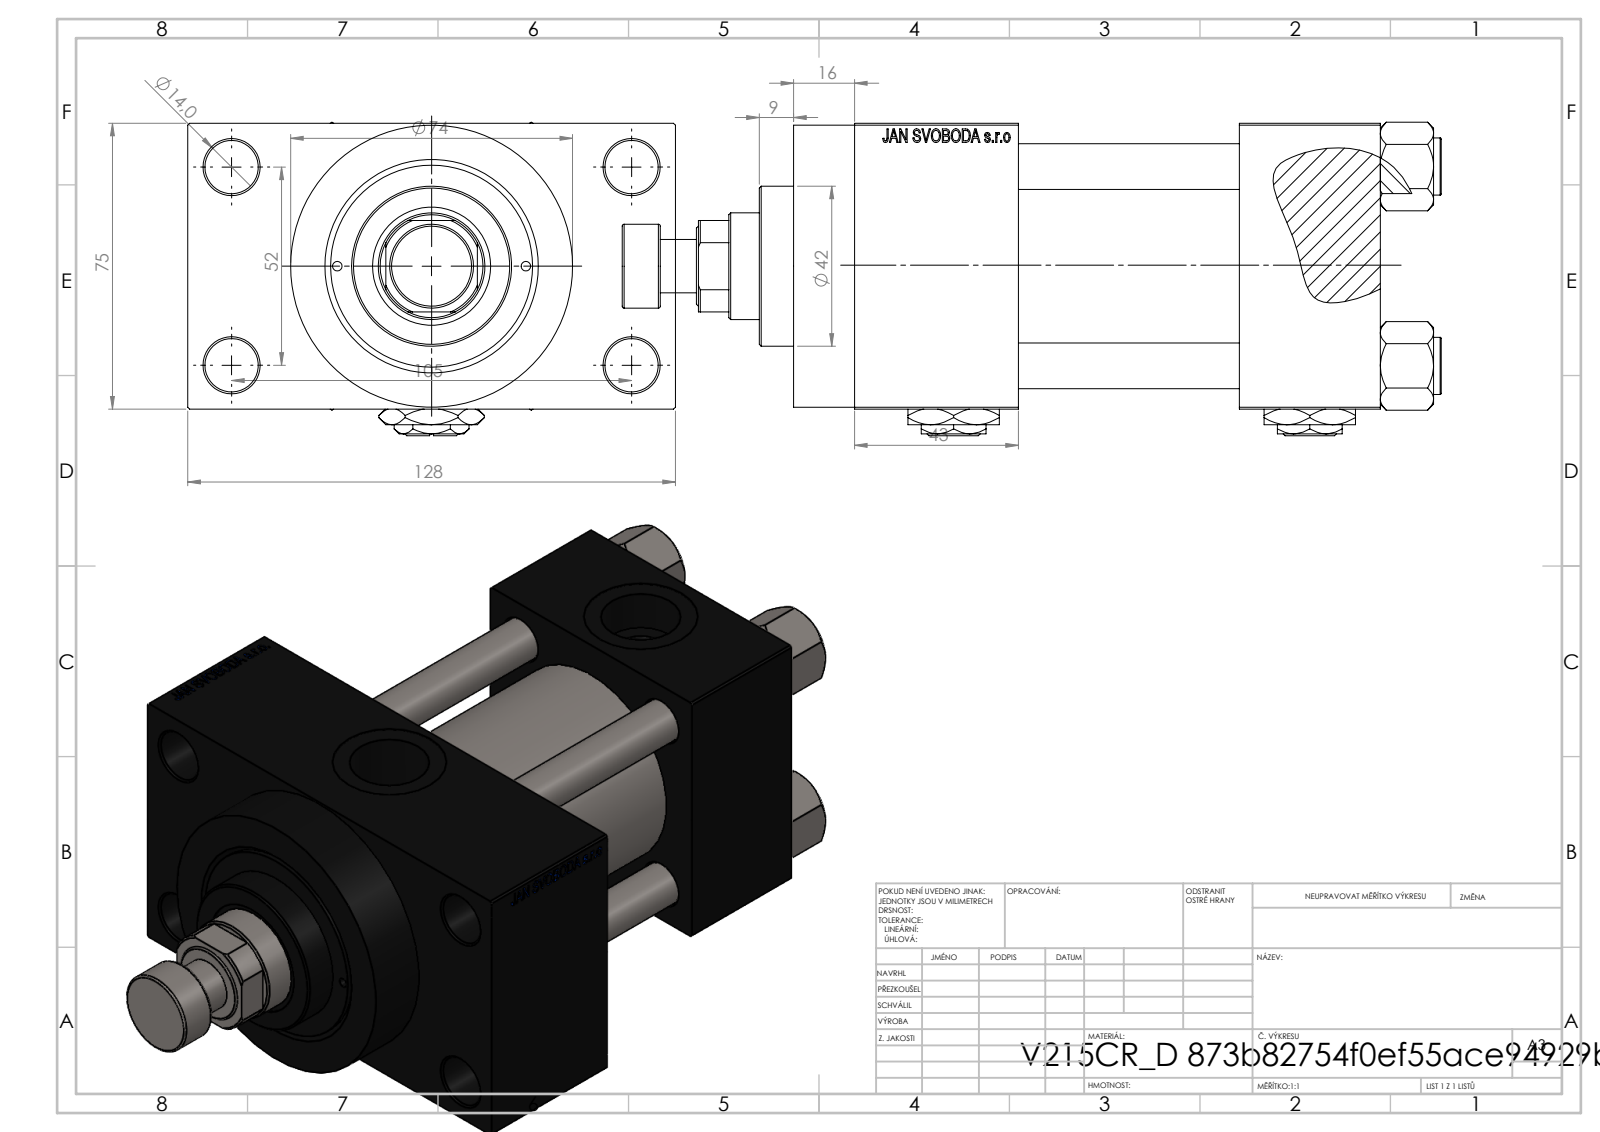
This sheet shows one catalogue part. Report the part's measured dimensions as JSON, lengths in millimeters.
{"part_name": "V215CR_D_Body; V215CR_ROD_END_W; V215_VC_A; Zatka_pro_OIL_PORT (+3 more)", "step_written_by": "SolidWorks 2019 (CONFIG_CONTROL_DESIGN)", "units": "millimeters", "bodies": {"solids": 14, "faces": 1219, "planar": 549, "cylindrical": 104, "other": 566}, "overall_size": [215, 128, 82.27], "volume_mm3": 816290, "surface_area_mm2": 175342, "round_holes": [[12, 4], [14, 4], [7, 2], [20.96, 2], [30, 2], [18.5, 1], [28, 1], [31, 1], [41, 1], [50, 1], [53, 1]], "round_bosses_or_shafts": [[15, 4], [74, 1], [56, 1], [42, 1], [22, 1], [14, 1]], "partial_cylinders_radius": [[13.5, 1]], "face_to_face_distances": [75, 58, 37, 95, 26.5, 101.5, 138, 101, 43, 16], "hole_center_spacings": [26.35, 36.98, 52.3, 58.43, 58.59, 78.65, 94.37, 52]}
